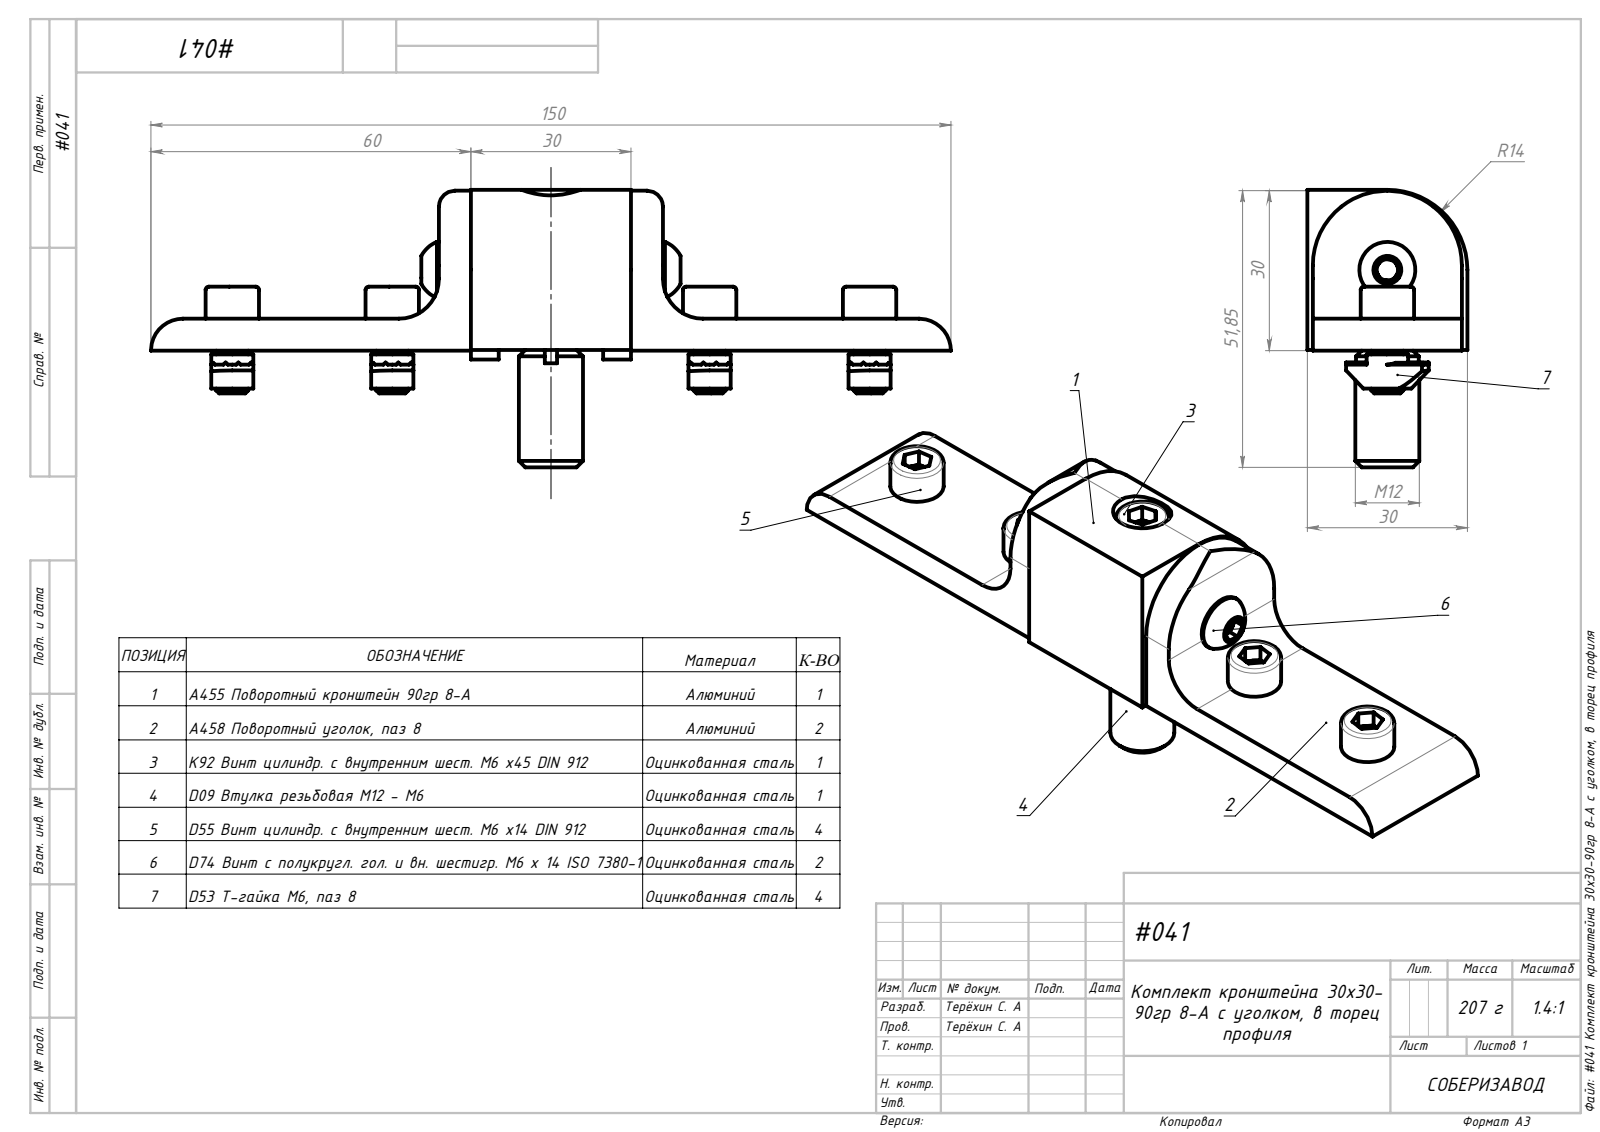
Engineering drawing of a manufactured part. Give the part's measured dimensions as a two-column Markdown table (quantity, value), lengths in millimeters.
| quantity | value |
| --- | --- |
| part name | K92 Винт цилиндр. с внутренним шест. М6 х45 DIN 912; D53 Т-гайка М6, паз 8_00; A458 Поворотный уголок, паз 8; #041 Комплект кронштейна 30х30-90гр 8-A с уголком, в торец профиля (+4 more) |
| STEP written by | SolidWorks 2021 (AUTOMOTIVE_DESIGN) |
| units | millimeters |
| bodies | 15 solids, 476 faces (269 planar, 85 cylindrical, 122 other) |
| overall size | 150 × 52 × 30 |
| volume | 59 547 mm³ |
| surface area | 25 852 mm² |
| round holes (diameter × count) | 6.3 × 5, 5 × 4, 5.1 × 1, 5.5 × 1, 6.25 × 1, 11 × 1 |
| round bosses / shafts (diameter × count) | 6 × 6, 10 × 5, 12 × 1, 10.5 × 1 |
| partial cylindrical surfaces (radius × count) | 4 × 8, 6.87 × 8, 3 × 2, 7.5 × 2, 14 × 2, 15 × 1 |
| main face-to-face distances | 6, 30, 5.85, 1.03, 28.98, 27.95, 36, 28.97, 1.02, 30.15 |
| hole center spacings | 29.75, 30, 59.75, 89.5, 59.5, 119.5 |
